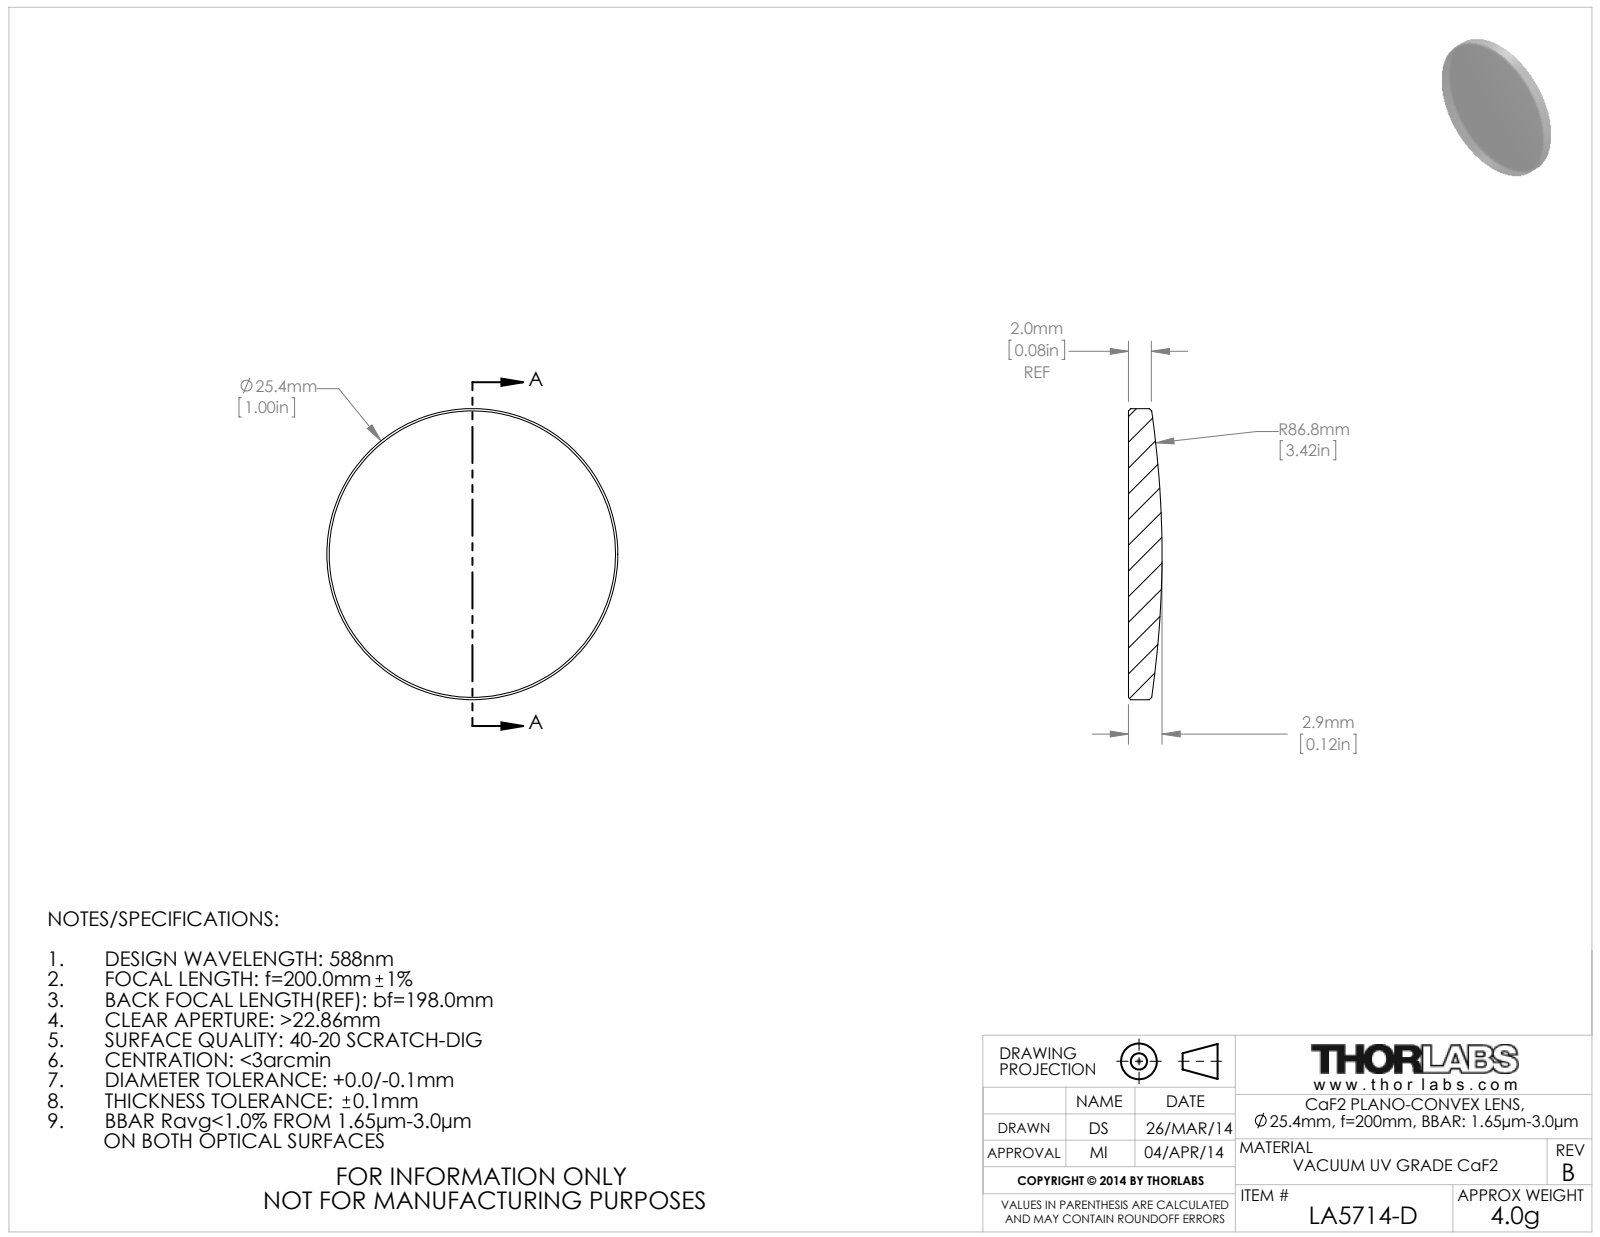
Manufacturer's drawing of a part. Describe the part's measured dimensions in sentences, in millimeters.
The part is named "22964-E0W". Its 3-D file was written by "SolidWorks 2011 (AUTOMOTIVE_DESIGN)". It is 0 solids with 5 faces: 1 planar, 2 cylindrical and 2 other. Overall it measures 25.4 by 25.4 by 2.93 millimeters. Round bosses or shafts: 1 of diameter 25.4.
